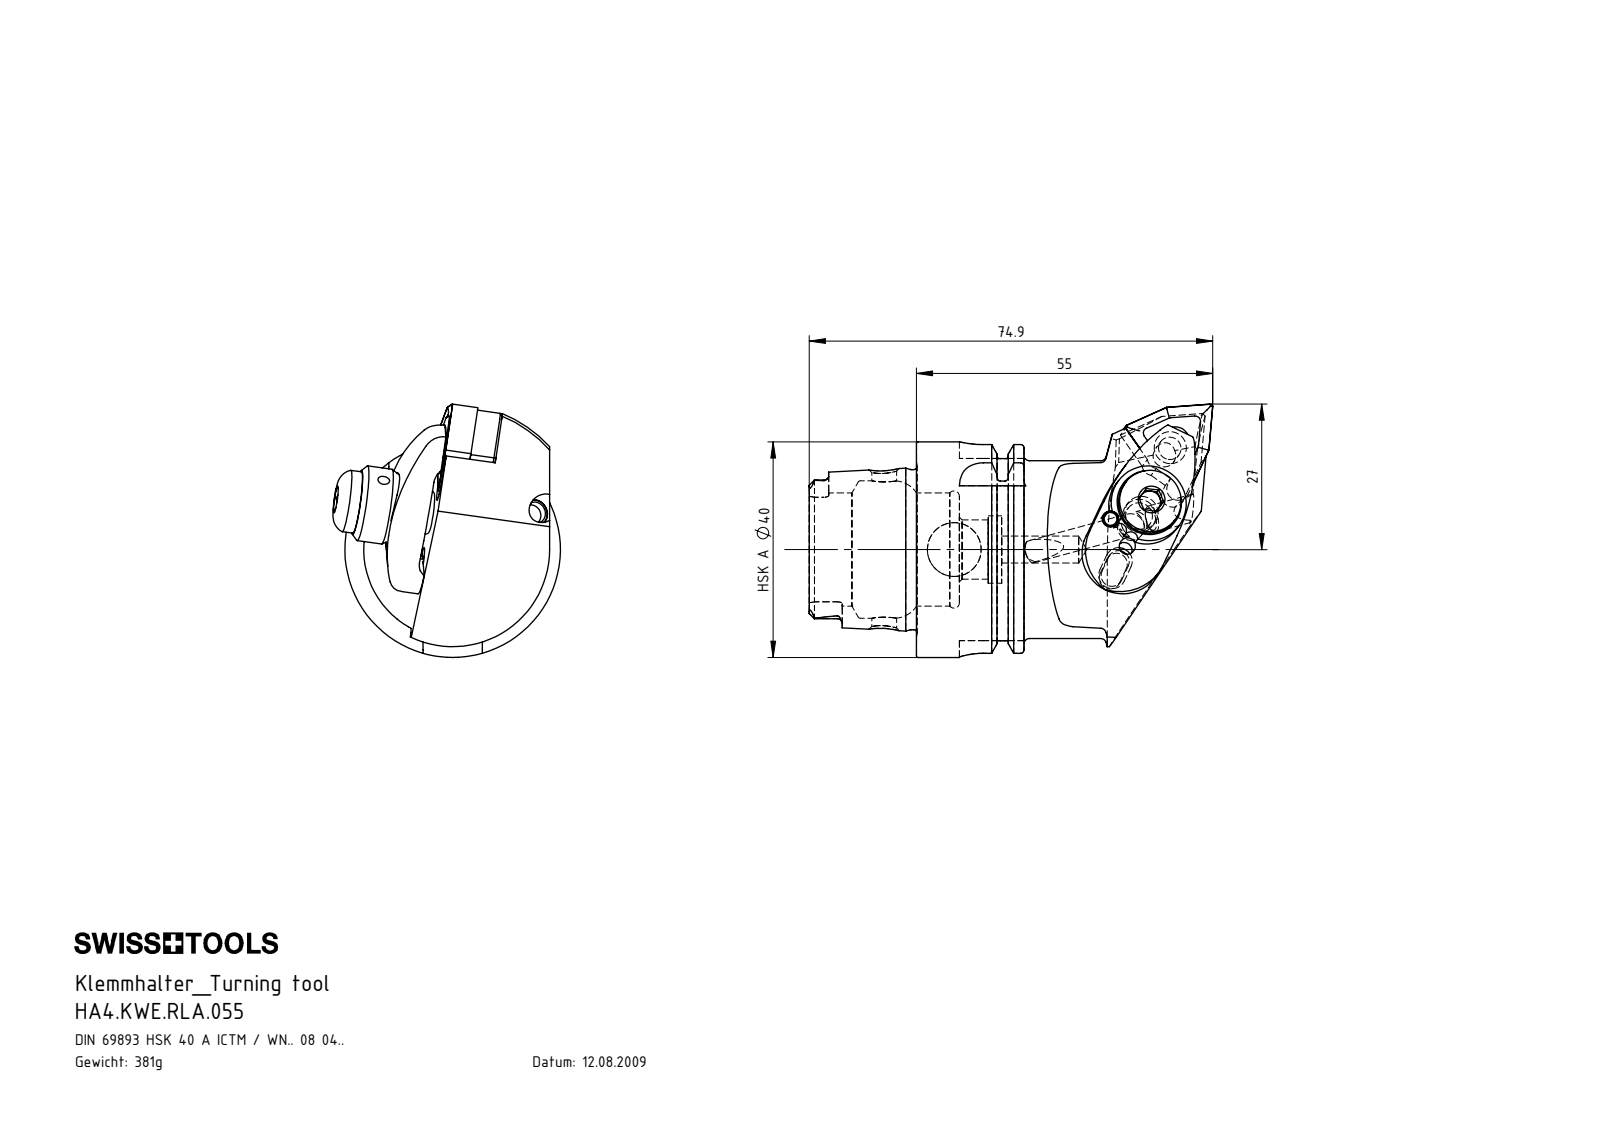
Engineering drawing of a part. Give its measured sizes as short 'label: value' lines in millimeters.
name: HA4.KWE.RLA.055; WCC-ER2.001.010_A; WNMG080404; WCC-ER3.102.024_C (+7 more)
written by: SolidWorks 2017 (AUTOMOTIVE_DESIGN)
unit: mm
bodies: 11 solids, 486 faces (133 planar, 157 cylindrical, 196 other)
size: 74.9 × 47 × 42.22
volume: 48 011 mm³; area: 19 072 mm²
holes: 3× ⌀2, 3× ⌀5, 2× ⌀4.2, 2× ⌀7, 1× ⌀2.4, 1× ⌀3, 1× ⌀4, 1× ⌀4.6, 1× ⌀5.16, 1× ⌀6.2, 1× ⌀6.7, 1× ⌀7.8
bosses: 2× ⌀5, 2× ⌀3, 1× ⌀40, 1× ⌀34.75, 1× ⌀33, 1× ⌀29.71, 1× ⌀14, 1× ⌀11.5
rounds: 6× R0.39, 6× R0.69, 6× R0.9, 4× R0.4, 4× R4.5, 3× R1.5, 3× R2, 3× R3
face distances: 9.25, 4.77, 7.95, 4.76, 10.52, 1.27, 19.95, 12, 4.48, 5.75
hole spacings: 15, 8, 14.82, 21.45, 5.62, 7.79, 7.8, 7.94
